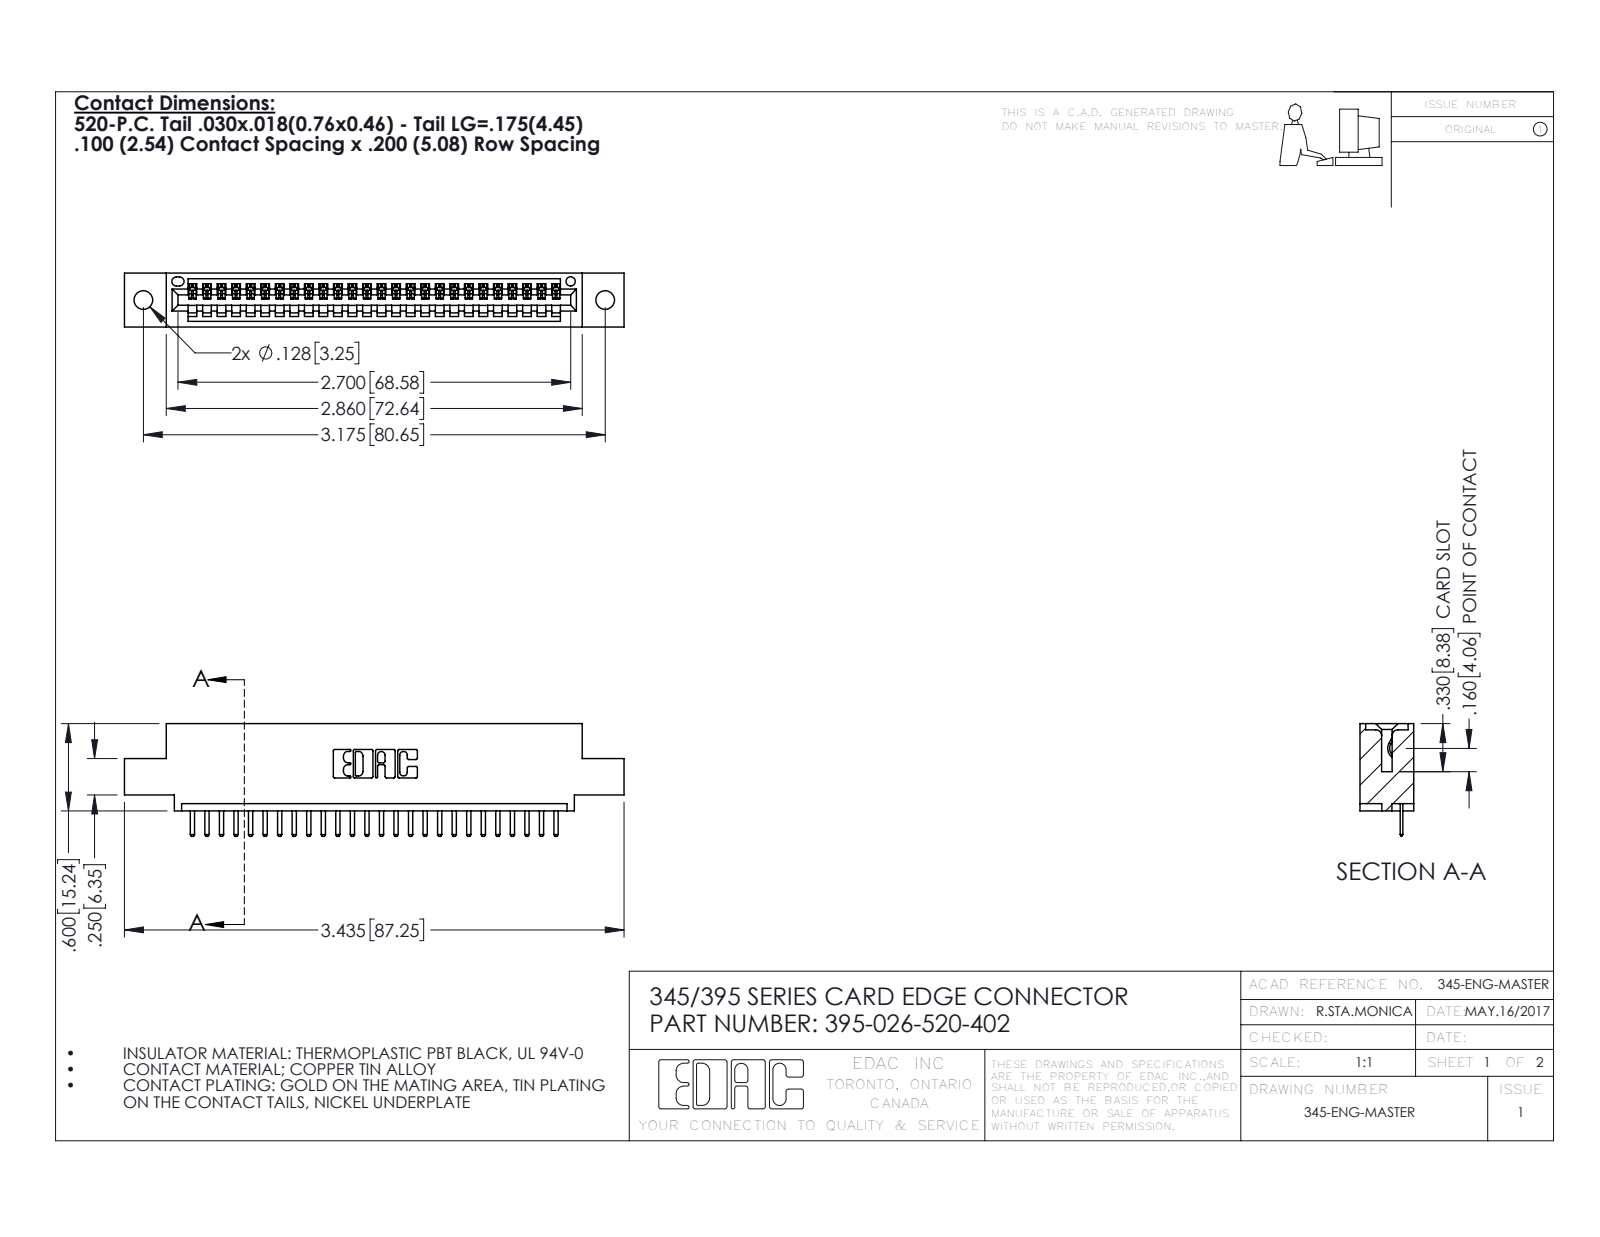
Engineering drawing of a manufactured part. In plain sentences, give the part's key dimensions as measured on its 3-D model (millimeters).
The part is named "345-292-001_345-293-120; 395-026-520-402; 345 Part_0.110 Offset - 0.128 Dia". Its 3-D file was written by "SolidWorks 2016 (CONFIG_CONTROL_DESIGN)". It is 27 solids with 1742 faces: 1176 planar, 566 cylindrical and 0 other. Overall it measures 87.2 by 19.7 by 9.4 millimeters. Its volume is 7 960 cubic millimeters and its surface area 9 942 square millimeters. Round holes: 2 of diameter 3.3, 1 of diameter 1.6. Partial cylindrical surfaces (rounded edges, fillets, slot ends): 54 of radius 0.3, 52 of radius 0.2, 22 of radius 0.3, 6 of radius 0.2, 6 of radius 0.8, 3 of radius 0.7, 2 of radius 0.8, 2 of radius 1. The main face-to-face distances are 7.6, 1.8, 9.4, 5.1, 2.5, 6.9, 0.6, 5.7, 1.8, 3.8. The hole center spacings are 6.9, 74.7, 80.6.
